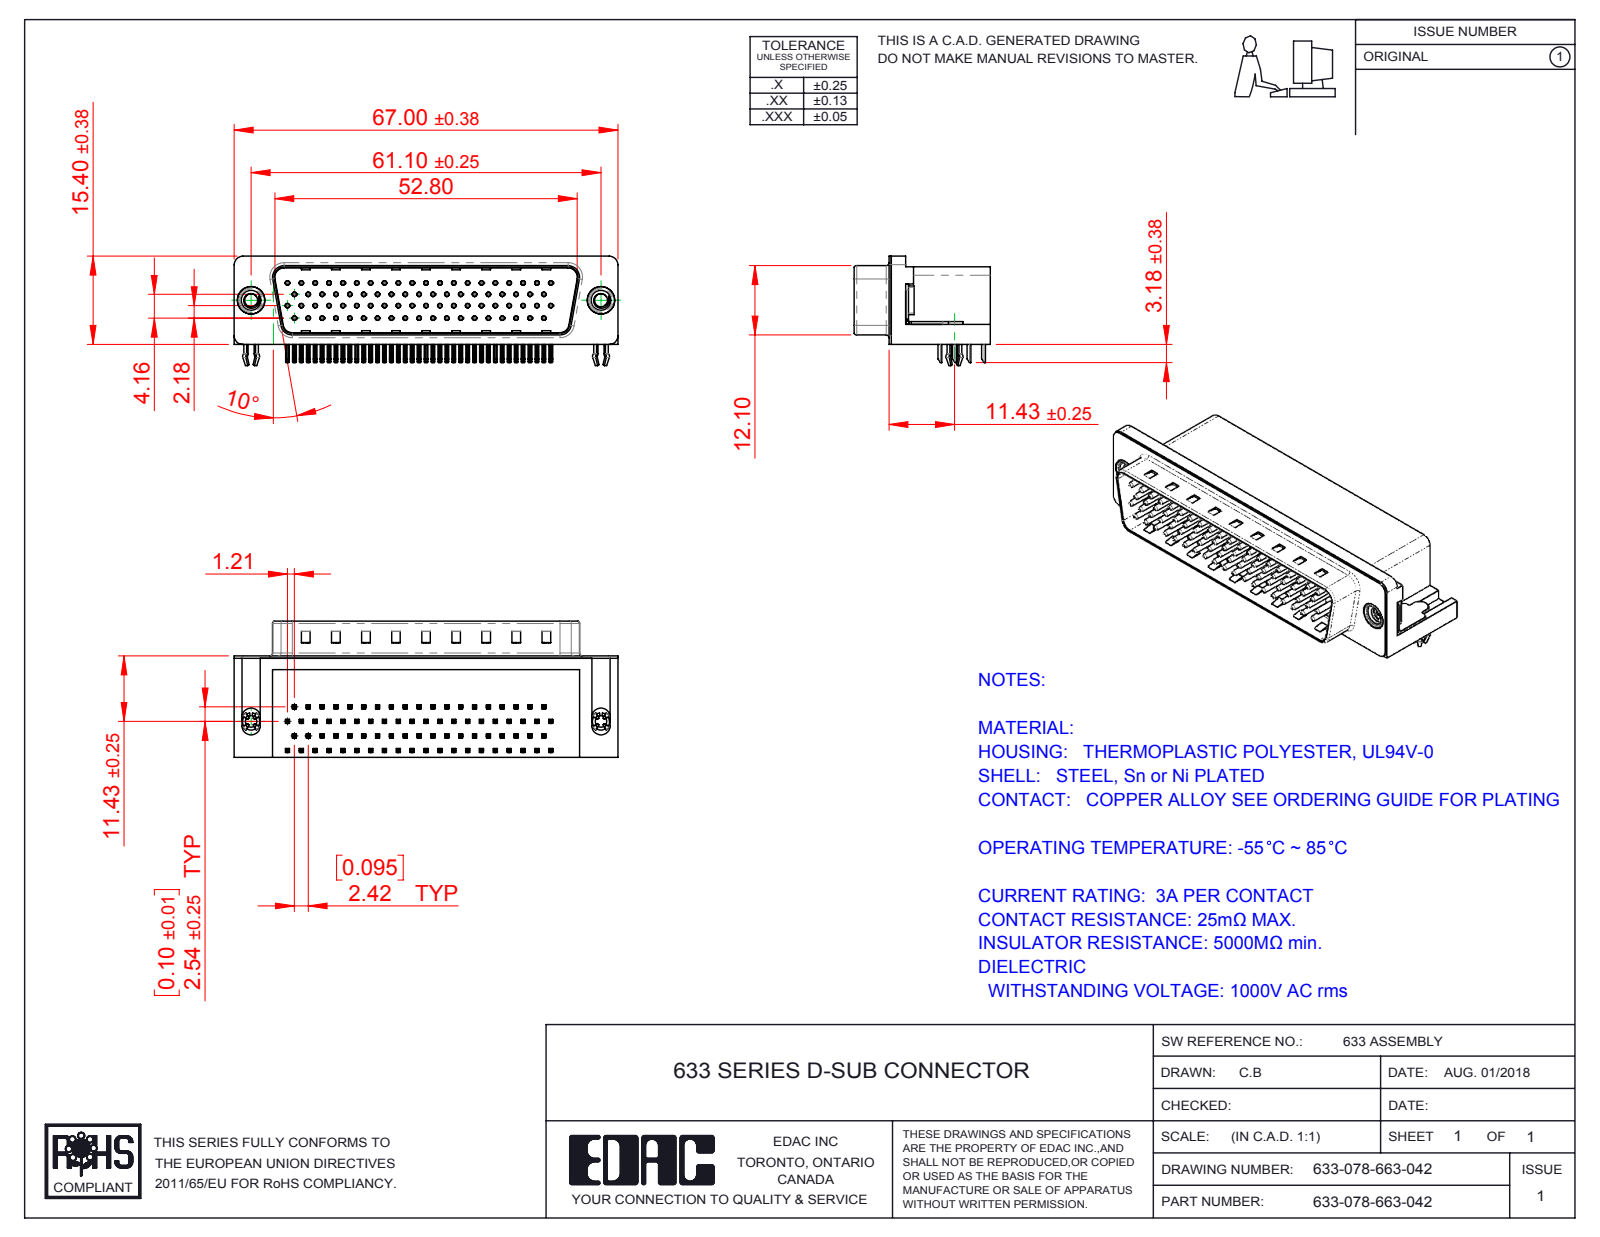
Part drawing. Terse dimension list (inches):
name: 633-078-663-042; 633 4-40 Threaded Rivet; 633 4 Prong Board Lock_78 Contact; 633 Contact Top 78 (+5 more)
written by: SolidWorks 2016 (CONFIG_CONTROL_DESIGN)
unit: in
bodies: 84 solids, 6396 faces (4023 planar, 1784 cylindrical, 589 other)
size: 2.638 × 0.937 × 0.752
volume: 0.892 in³; area: 25.47 in²
holes: 78× ⌀0.014, 78× ⌀0.031, 2× ⌀0.079, 2× ⌀0.089, 2× ⌀0.157, 2× ⌀0.189, 2× ⌀0.197
bosses: 78× ⌀0.03, 2× ⌀0.193, 2× ⌀0.187, 2× ⌀0.154, 2× ⌀0.118
rounds: 324× R0.01, 156× R0.005, 16× R0.039, 9× R0.02, 8× R0.063, 6× R0.059, 4× R0.018, 4× R0.035
face distances: 0.016, 0.52, 0.681, 0.461, 0.526, 0.081, 0.541, 0.065, 0.073, 0.469
hole spacings: 0.095, 0.191, 0.286, 0.381, 0.246, 0.281, 0.476, 0.339
